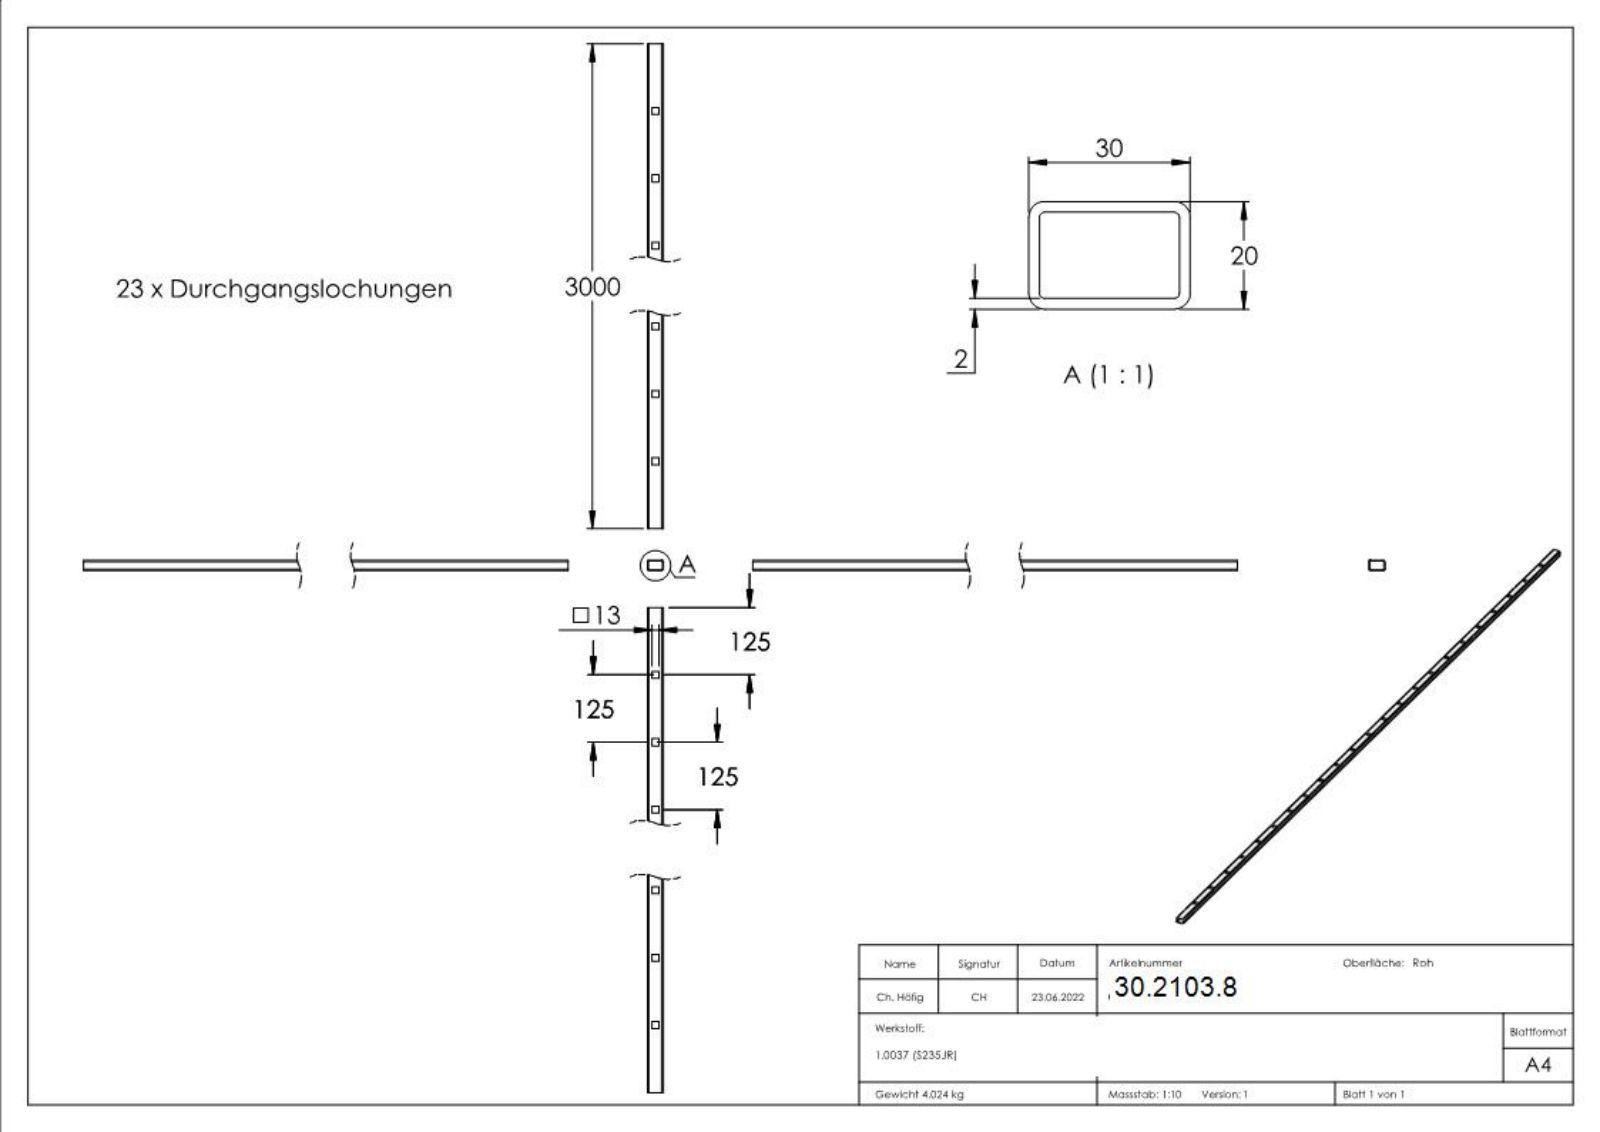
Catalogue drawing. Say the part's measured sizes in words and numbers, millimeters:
The part is named "69901". Its 3-D file was written by "SolidWorks 2018 (CONFIG_CONTROL_DESIGN)". It is 1 solid with 418 faces: 306 planar, 8 cylindrical and 104 other. Overall it measures 3000 by 30 by 20 millimeters. Its volume is 515 849 cubic millimeters and its surface area 520 999 square millimeters. Partial cylindrical surfaces (rounded edges, fillets, slot ends): 4 of radius 1, 4 of radius 3. The main face-to-face distances are 2, 18, 28, 20, 16, 30, 26, 8.5, 21.5, 6.5.
